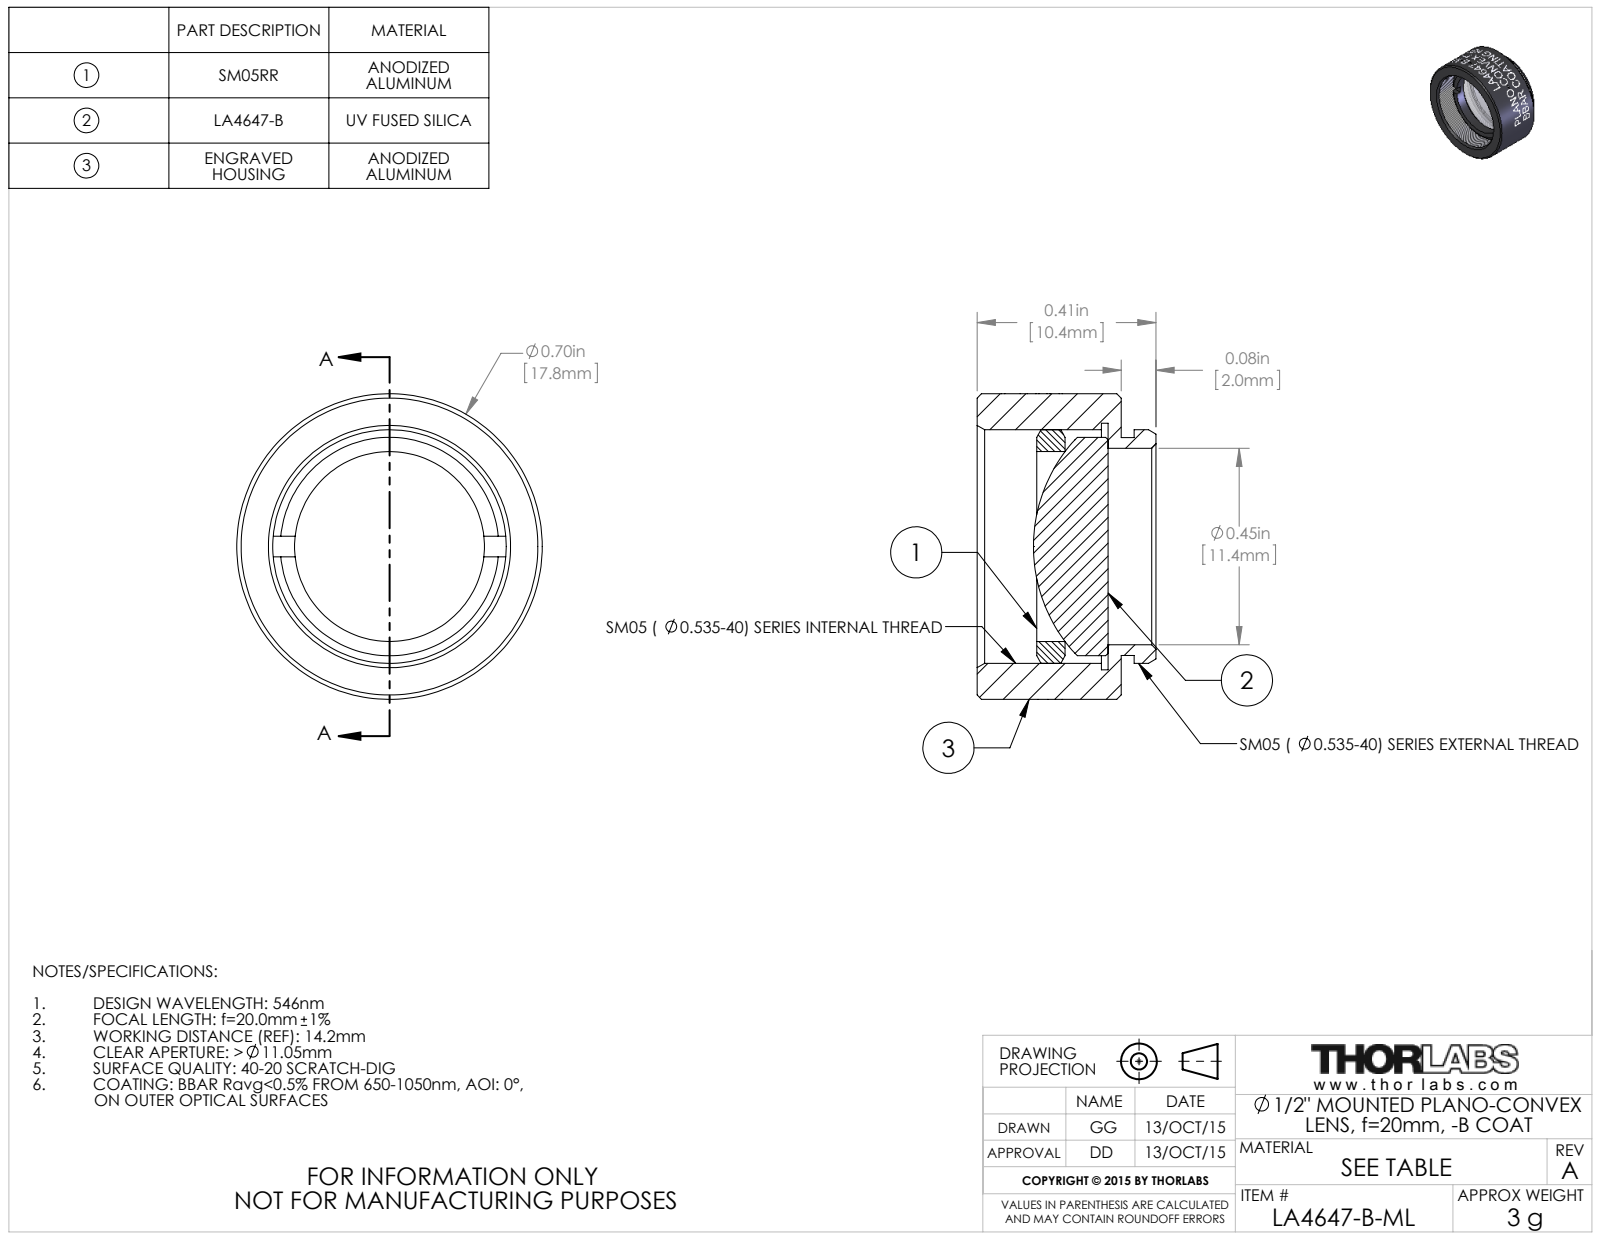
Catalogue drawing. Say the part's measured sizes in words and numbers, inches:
The part is named "TTN039336-E0W". Its 3-D file was written by "SolidWorks 2014 (CONFIG_CONTROL_DESIGN)". It is 3 solids with 149 faces: 16 planar, 112 cylindrical and 21 other. Overall it measures 0.7 by 0.7 by 0.41 inches. Its volume is 0.087 cubic inches and its surface area 2.877 square inches. Round holes: 1 of diameter 0.435, 1 of diameter 0.45, 1 of diameter 0.535, 1 of diameter 0.565. Round bosses or shafts: 1 of diameter 0.7, 1 of diameter 0.535, 1 of diameter 0.5, 1 of diameter 0.499. The main face-to-face distances are 0.03, 0.33, 0.3, 0.128, 0.098, 0.202, 0.193, 0.163, 0.065, 0.137.
